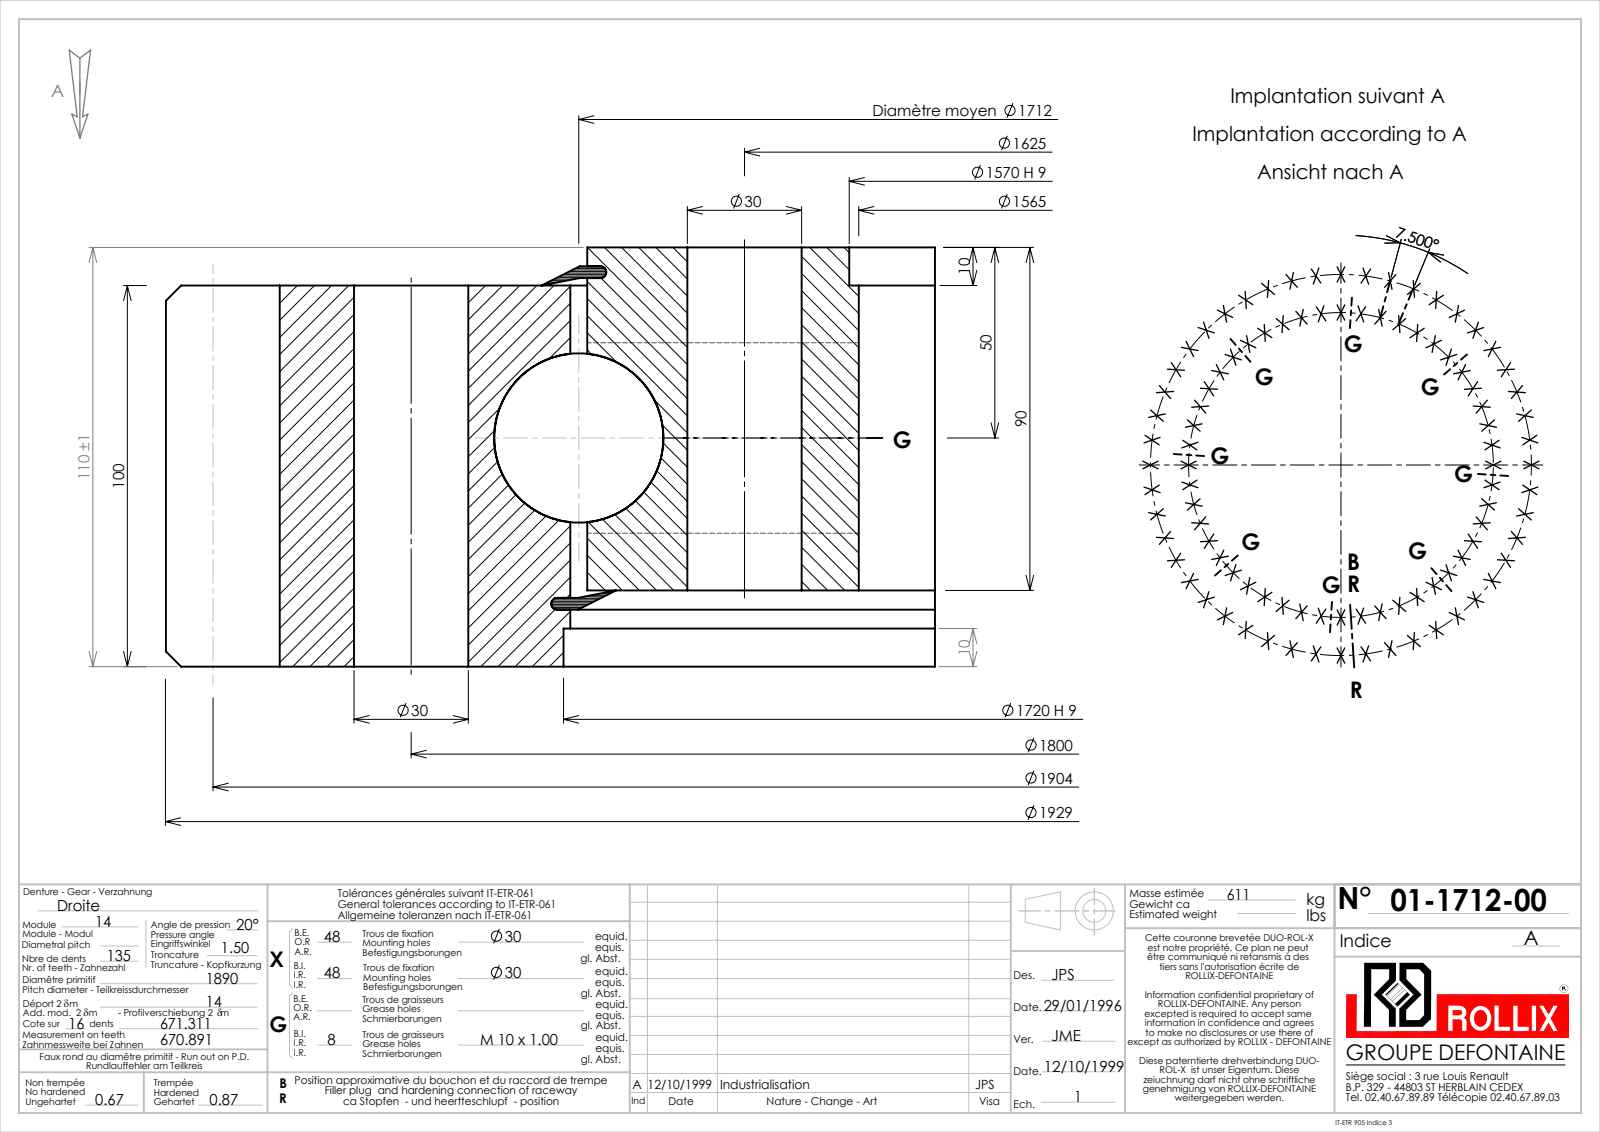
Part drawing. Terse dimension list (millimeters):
name: 01-1712-00
written by: SolidWorks 2016 (CONFIG_CONTROL_DESIGN)
unit: mm
bodies: 5 solids, 1080 faces (284 planar, 497 cylindrical, 299 other)
size: 1928.98 × 1928.87 × 110
volume: 71 870 000 mm³; area: 5 869 000 mm²
holes: 96× ⌀30, 8× ⌀9, 1× ⌀1565, 1× ⌀1570, 1× ⌀1716.44, 1× ⌀1720
bosses: 1× ⌀1707.56
rounds: 1× R934.5, 1× R964.5
face distances: 100, 10, 20, 80, 90, 110, 1.95, 81.95, 3.1, 5.05
hole spacings: 351.16, 688.83, 900, 117.72, 796.12, 1186.82, 117.73, 234.95
